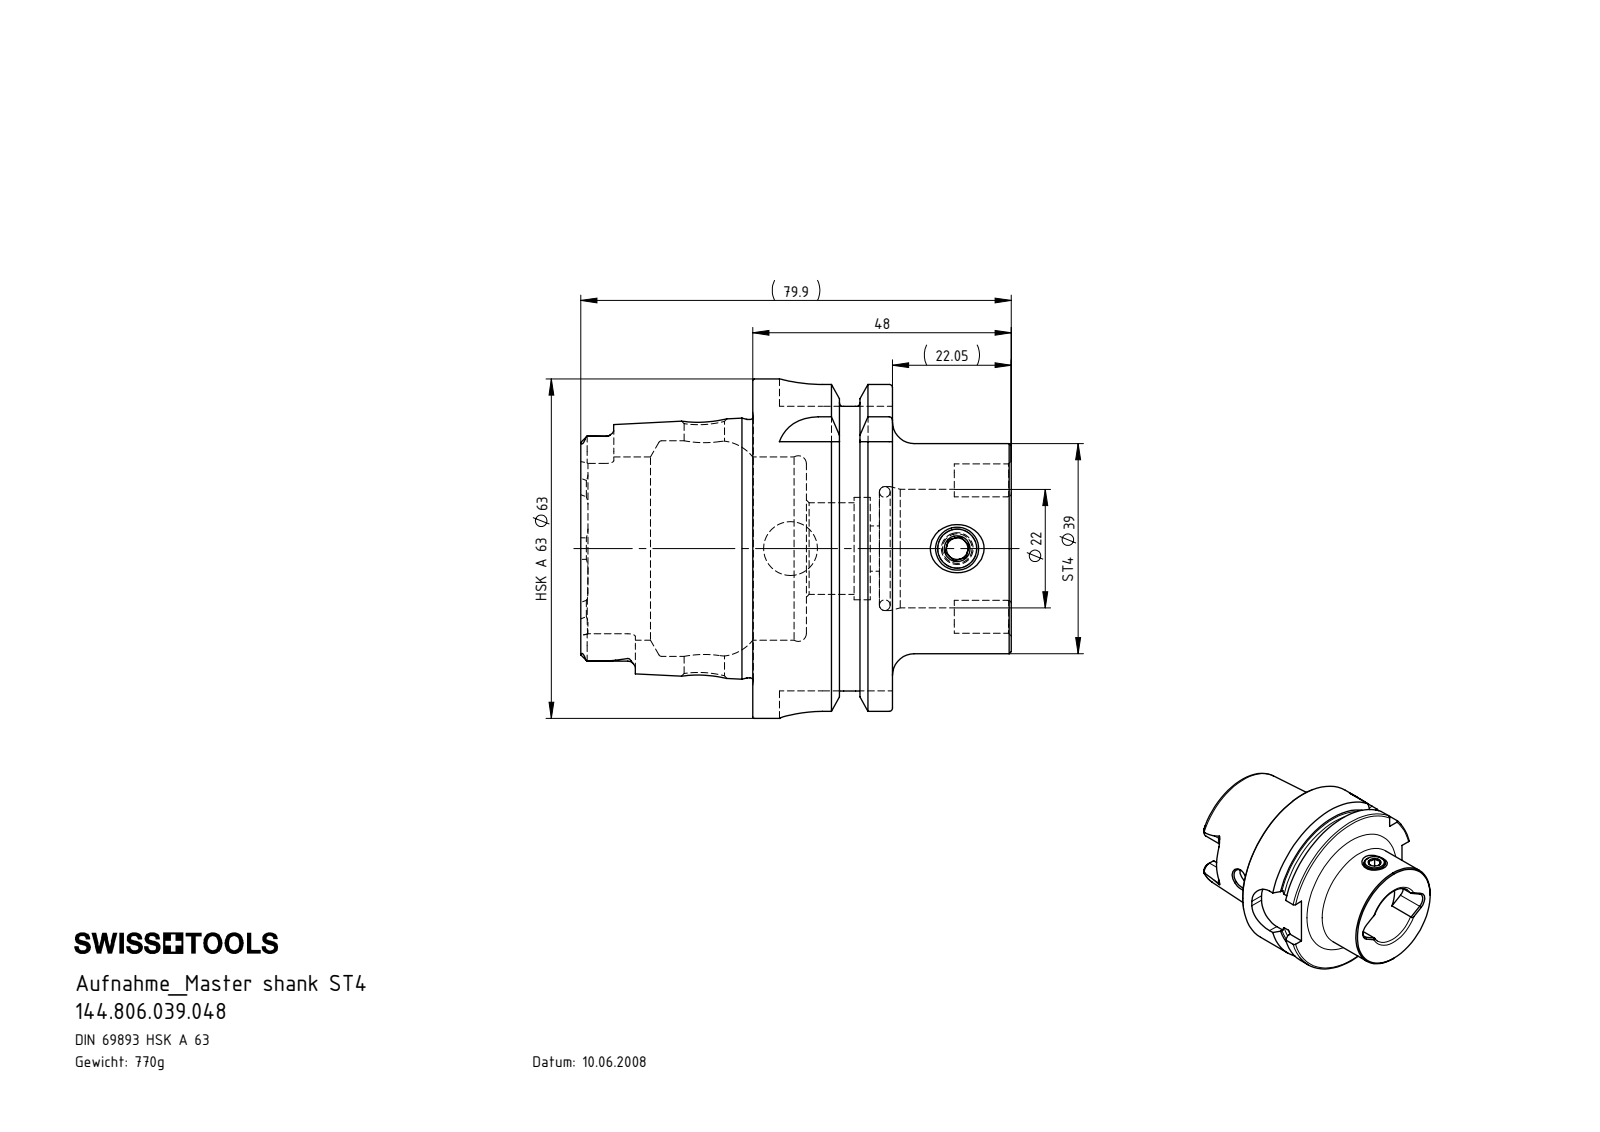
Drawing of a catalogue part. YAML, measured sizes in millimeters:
part_name: "ST4-ER1.001.011_A; HA6-ST4.K01.048_B_Fertigbearbeitung; DIN 3771 - 19x2; 144.806.039.048"
step_written_by: "SolidWorks 2017 (CONFIG_CONTROL_DESIGN)"
units: millimeters
bodies: {solids: 3, faces: 227, planar: 69, cylindrical: 58, other: 100}
overall_size: [79.9, 63, 63]
volume: 98281
surface_area: 27357
round_holes:
  - {diameter: 4, count: 1}
  - {diameter: 7.25, count: 1}
  - {diameter: 7.5, count: 1}
  - {diameter: 8.4, count: 1}
  - {diameter: 10, count: 1}
  - {diameter: 17, count: 1}
  - {diameter: 19, count: 1}
  - {diameter: 22, count: 1}
  - {diameter: 23, count: 1}
  - {diameter: 34, count: 1}
  - {diameter: 40, count: 1}
round_bosses_or_shafts:
  - {diameter: 63, count: 1}
  - {diameter: 54.95, count: 1}
  - {diameter: 47.94, count: 1}
  - {diameter: 39, count: 1}
  - {diameter: 8, count: 1}
partial_cylinders:
  - {radius: 1.4, count: 6}
  - {radius: 2.88, count: 4}
  - {radius: 8, count: 4}
  - {radius: 3.2, count: 2}
face_to_face_distances: [25.95, 48, 22.05, 16, 9.95, 38.05, 31.9, 41.85, 57.85, 79.9]
hole_center_spacings: [30.95]
